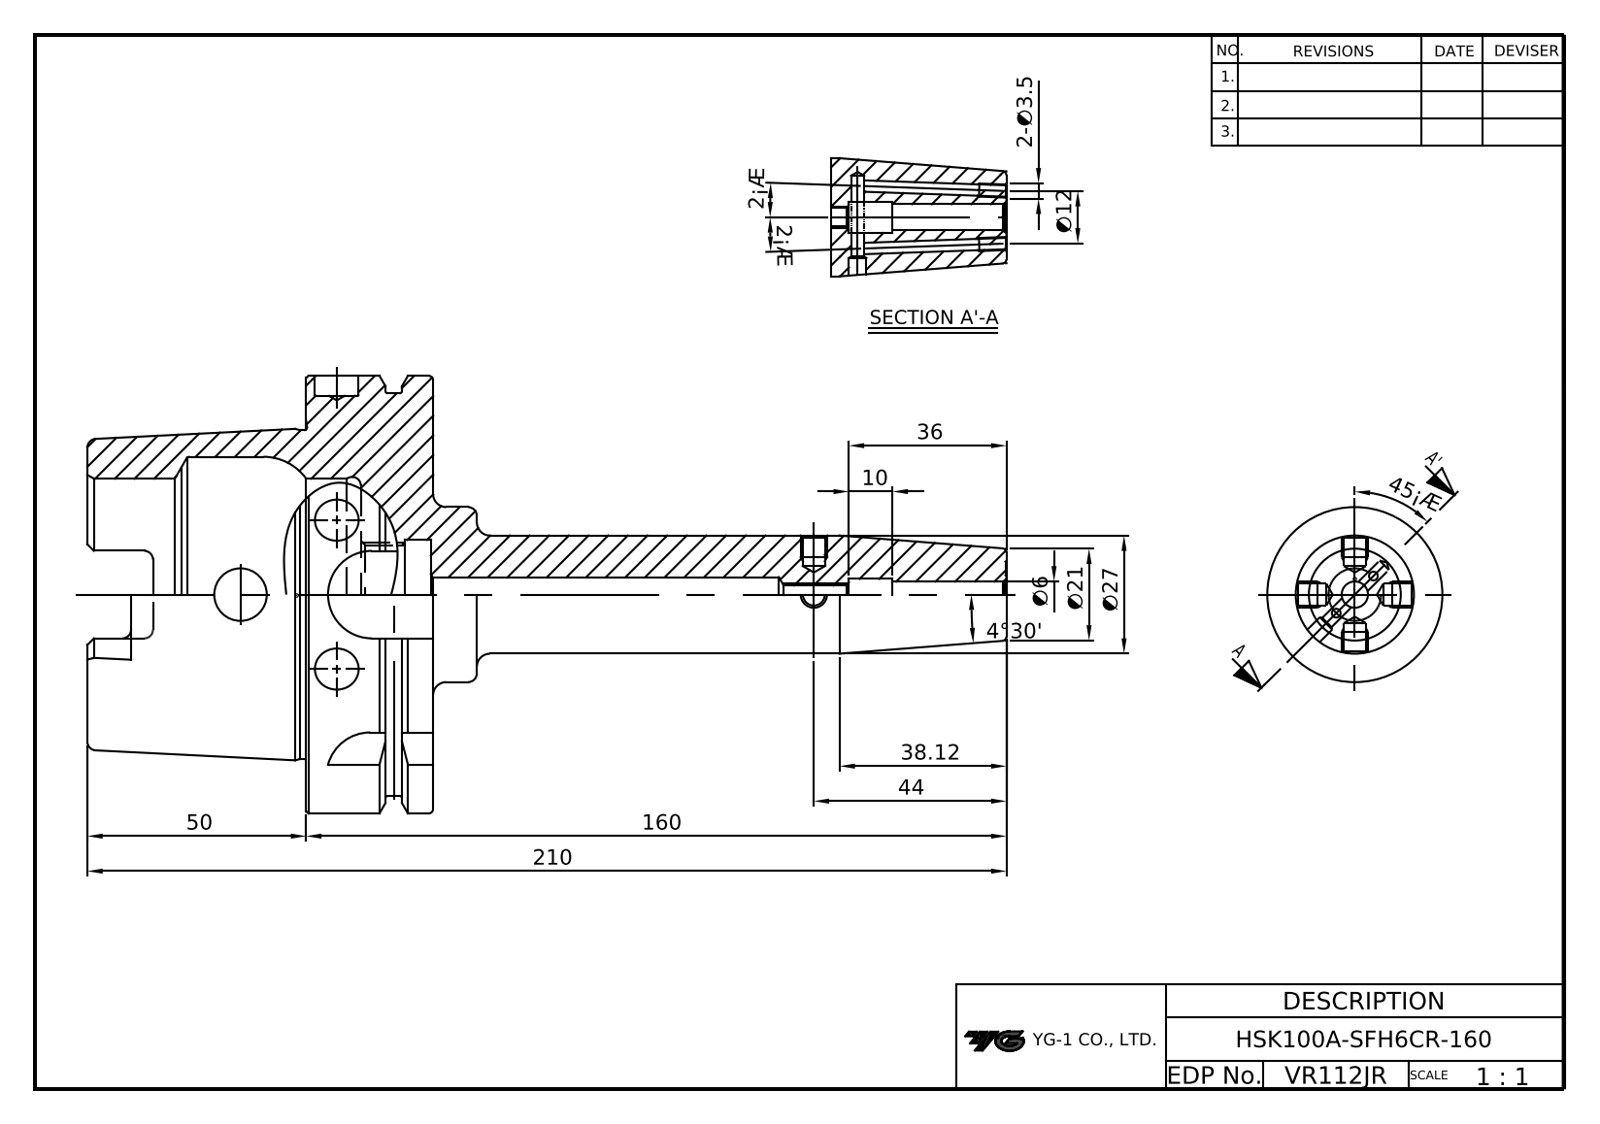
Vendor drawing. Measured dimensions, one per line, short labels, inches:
name: LO-HSK100A-SFH6CR-160
written by: Autodesk Inventor 2024 (AUTOMOTIVE_DESIGN)
unit: in
bodies: 1 solid, 124 faces (39 planar, 38 cylindrical, 47 other)
size: 8.268 × 3.937 × 3.937
volume: 19.6 in³; area: 100.2 in²
holes: 2× ⌀0.097, 2× ⌀0.472, 1× ⌀0.169, 1× ⌀0.236, 1× ⌀0.283, 1× ⌀0.394, 1× ⌀0.881, 1× ⌀0.984, 1× ⌀2.087, 1× ⌀2.48
bosses: 1× ⌀3.937, 1× ⌀3.622, 1× ⌀2.969, 1× ⌀1.575, 1× ⌀1.063
rounds: 6× R0.079, 4× R0.192, 4× R0.394
face distances: 1.142, 0.492, 0.65, 3.11, 2.461, 1.969, 0.394, 3.465, 3.091, 1.122
